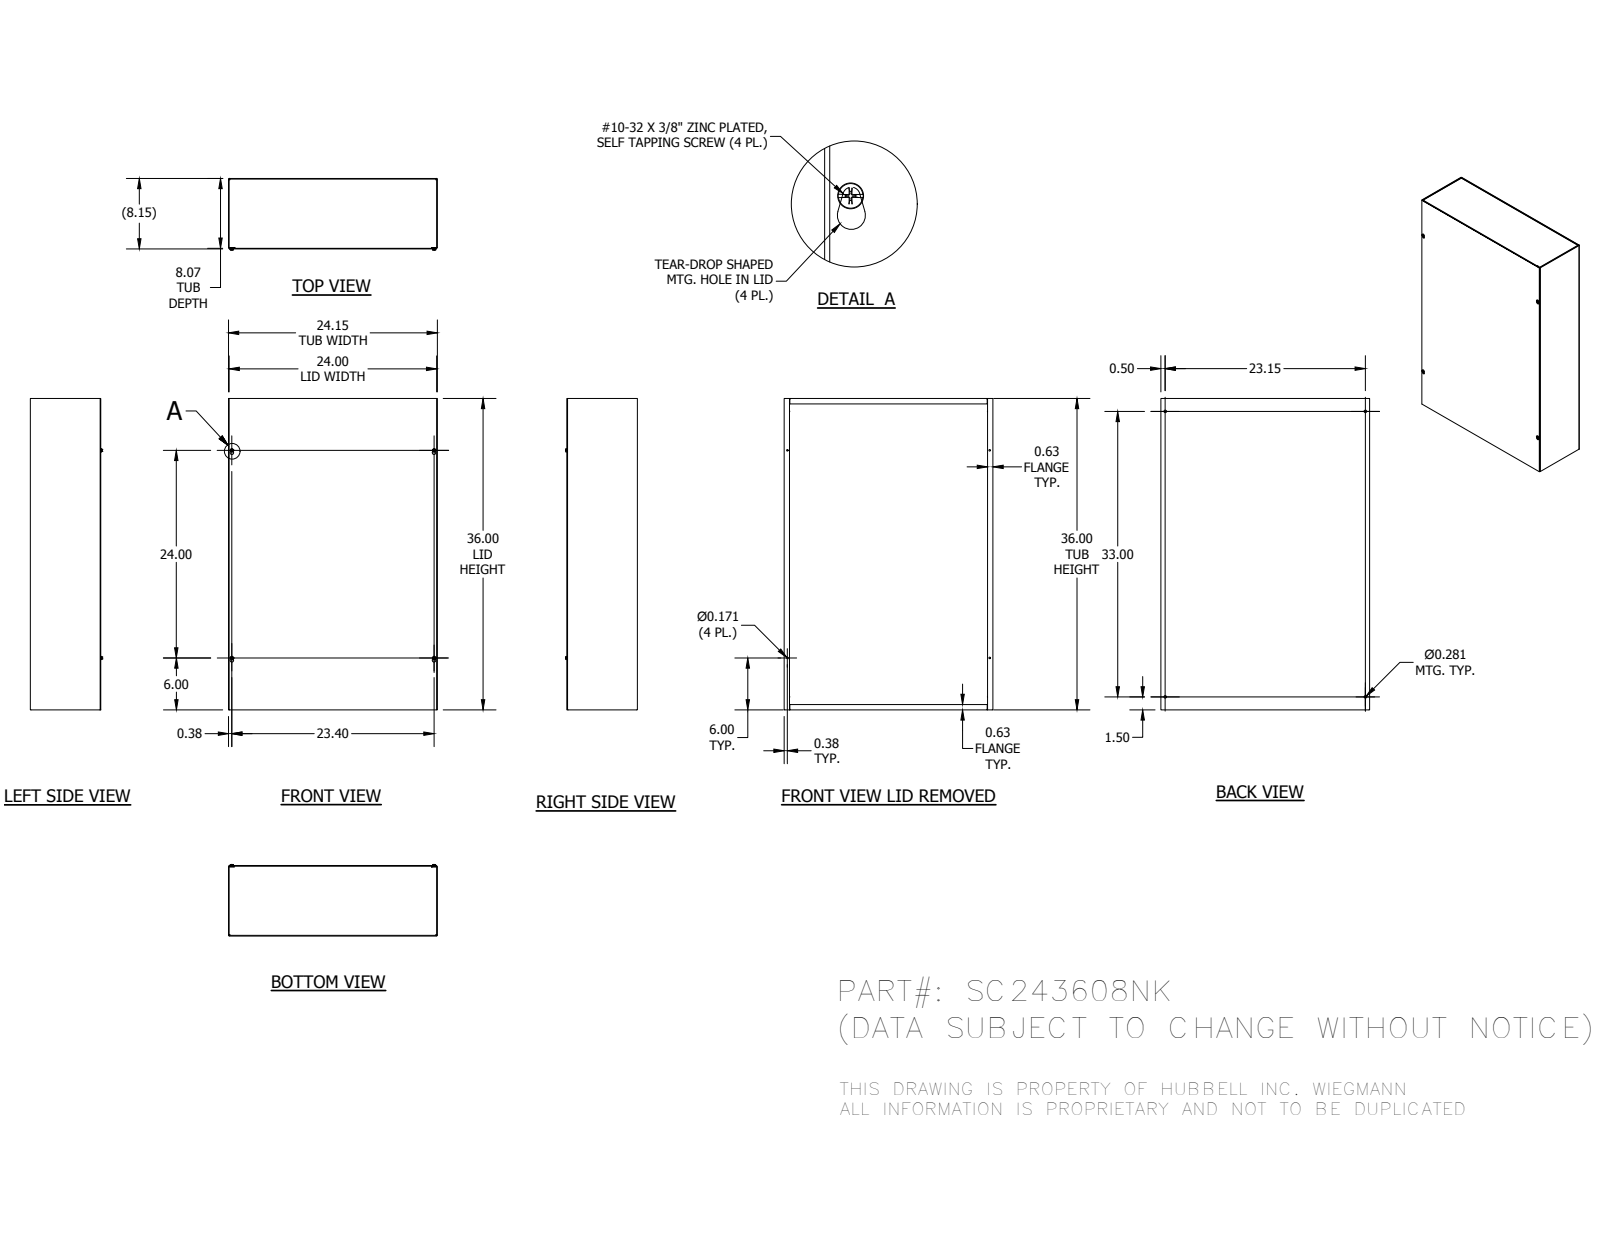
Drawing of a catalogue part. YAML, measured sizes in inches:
part_name: "SC243608NKBLR; SC2408NKTB; SC2436LPA; 37214 (+1 more)"
step_written_by: "Autodesk Inventor 2014 (AUTOMOTIVE_DESIGN)"
units: inches
bodies: {solids: 8, faces: 320, planar: 192, cylindrical: 44, other: 84}
overall_size: [36, 24.148, 8.28]
volume: 206.9
surface_area: 5622
round_holes:
  - {diameter: 0.171, count: 4}
  - {diameter: 0.281, count: 4}
round_bosses_or_shafts:
  - {diameter: 0.19, count: 4}
partial_cylinders:
  - {radius: 0.016, count: 12}
  - {radius: 0.09, count: 12}
  - {radius: 0.125, count: 4}
  - {radius: 0.203, count: 4}
face_to_face_distances: [0.074, 8.074, 8, 8.148, 24.074, 35.926, 24, 24.148, 36, 35.852]
hole_center_spacings: [4.502, 23.704, 28.5, 36.795, 23.148, 23.398, 24, 33]
